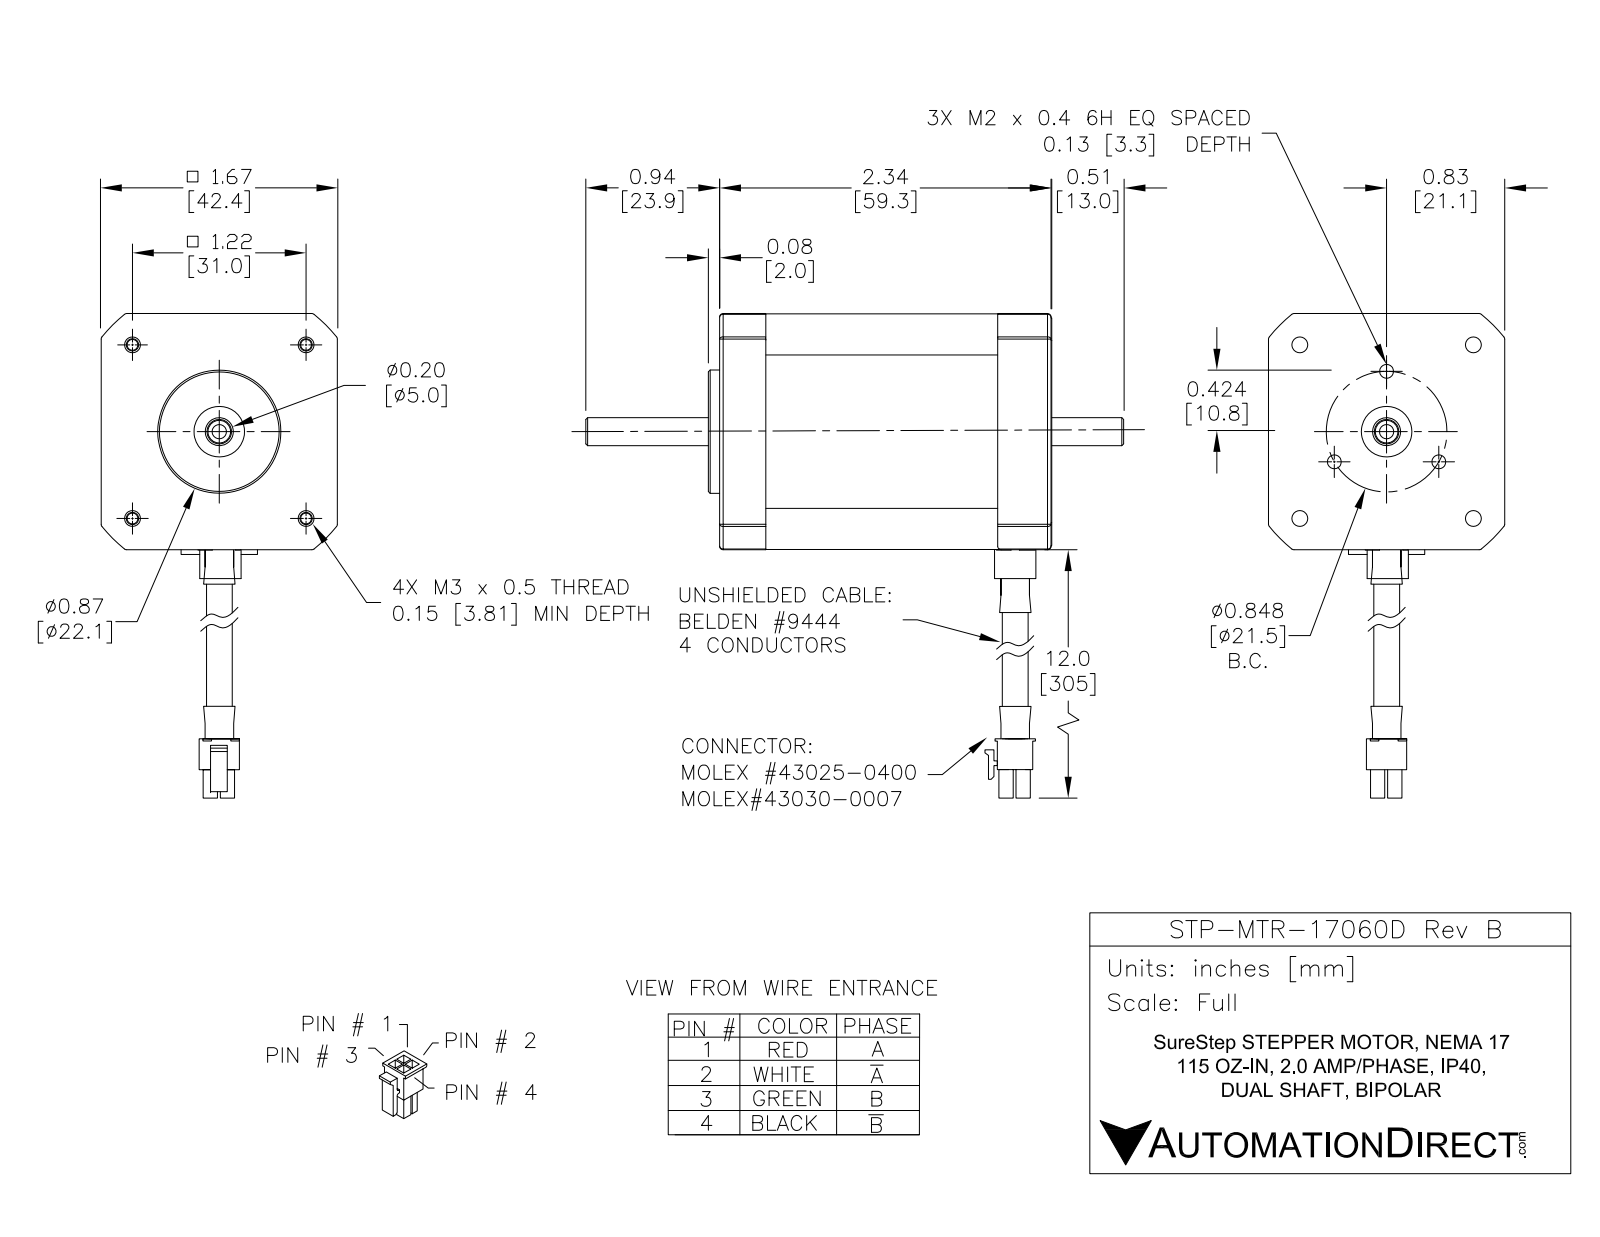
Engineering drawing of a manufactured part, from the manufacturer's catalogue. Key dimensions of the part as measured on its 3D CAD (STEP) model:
Part name (STEP PRODUCT): STP-MTR-17060E
STEP written by: SolidWorks 2017 (AUTOMOTIVE_DESIGN)
Units: inches
Bodies: 8 solids, 428 faces (258 planar, 112 cylindrical, 58 other)
Overall size (bounding box): 13.976 × 3.78 × 1.66
Volume: 6.675 in³ · Surface area: 35.01 in²
Round holes (diameter × count): ⌀0.086 ×4, ⌀0.15 ×4, ⌀0.079 ×3, ⌀0.05 ×1, ⌀0.25 ×1, ⌀0.355 ×1
Round bosses / shafts (diameter × count): ⌀0.13 ×4, ⌀0.866 ×1, ⌀0.29 ×1, ⌀0.217 ×1, ⌀0.197 ×1
Partial cylindrical surfaces — rounded edges, fillets, slot ends (radius × count): R0.025 ×17, R0.012 ×3, R0.006 ×1, R0.147 ×1, R0.986 ×1, R0.988 ×1, R1.025 ×1, R1.06 ×1
Main face-to-face distances: 1.656, 1.658, 2.335, 1.66, 0.118, 2.414, 0.079, 0.098, 0.089, 0.145
Hole centre spacings: 1.22, 0.863, 0.424, 0.466, 0.734, 0.857, 1.055, 1.201
